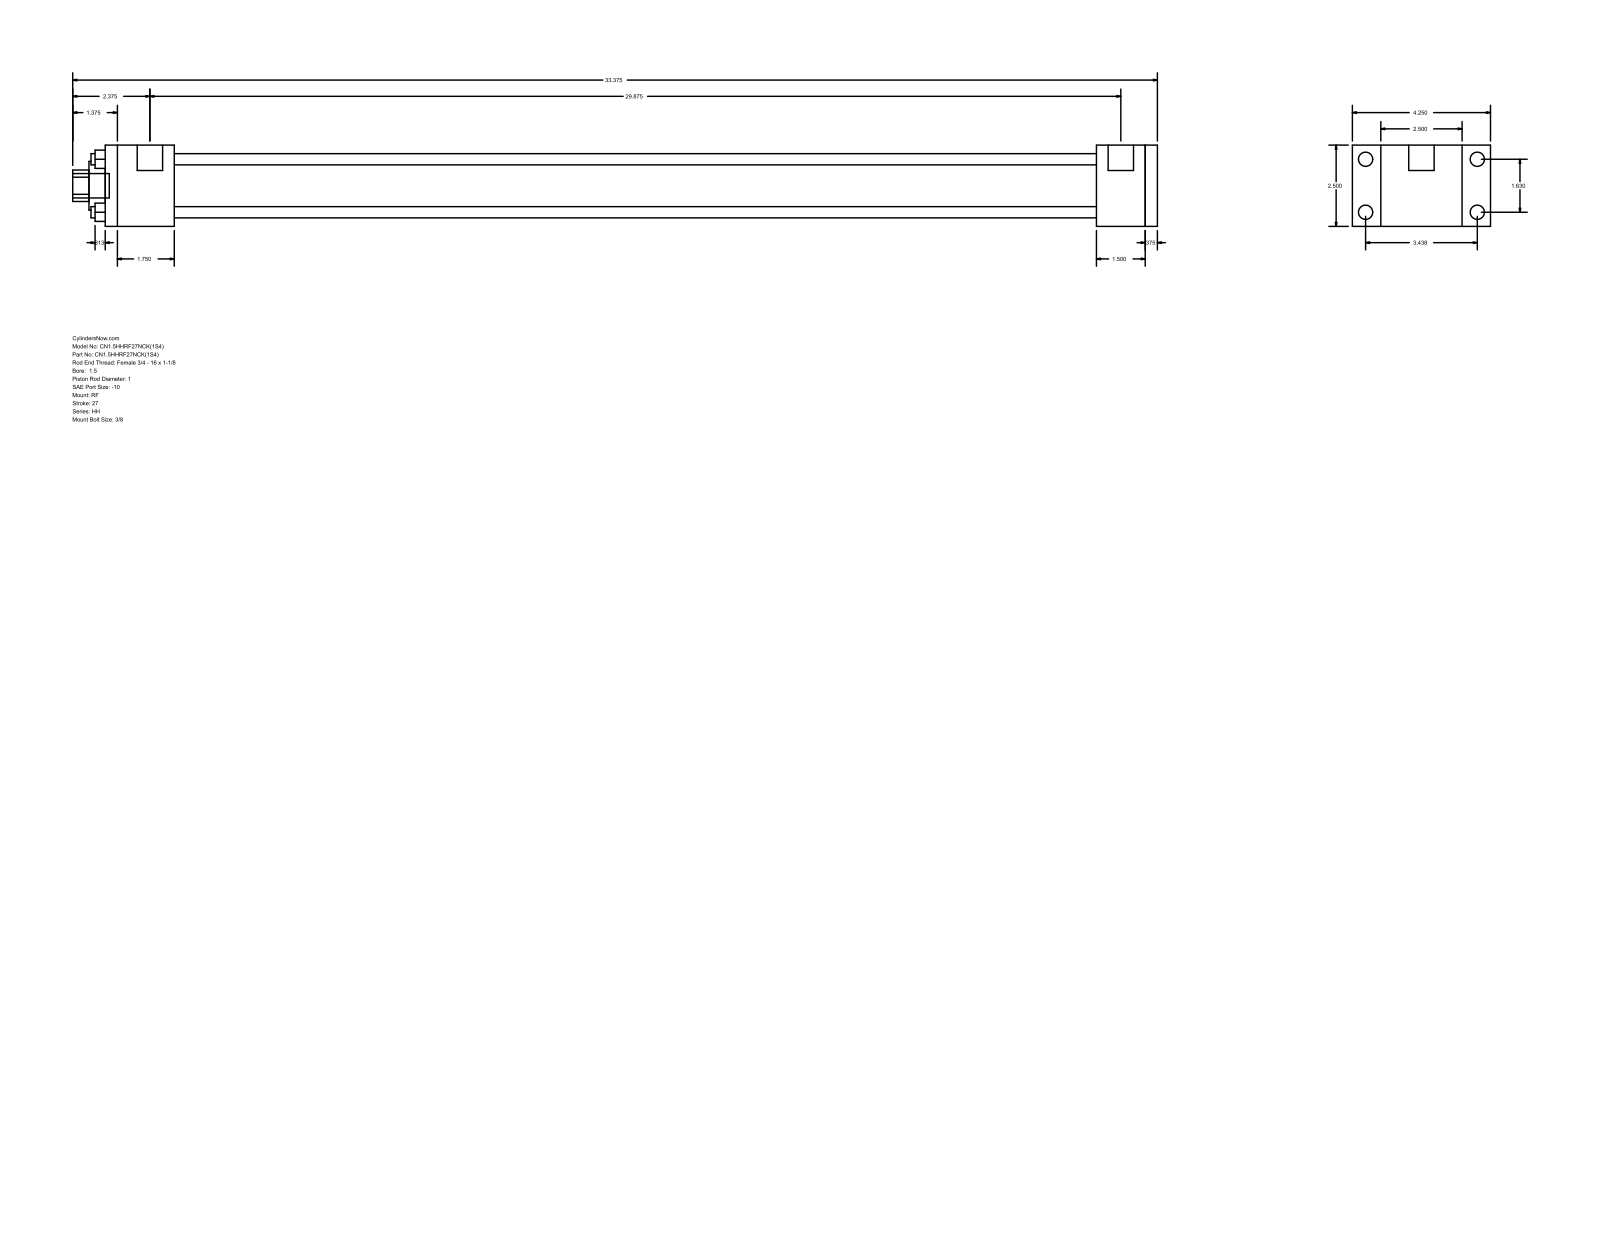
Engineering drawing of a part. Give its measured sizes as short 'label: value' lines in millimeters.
name: HH_RF__0150_1
written by: GSSL Pune (CONFIG_CONTROL_DESIGN)
unit: mm
bodies: 0 solids, 92 faces (64 planar, 28 cylindrical, 0 other)
size: 847.73 × 107.95 × 63.5
holes: 4× ⌀8.76, 1× ⌀25.4, 1× ⌀38.1, 1× ⌀44.45
bosses: 4× ⌀11.13, 4× ⌀5.56, 2× ⌀19.84, 1× ⌀19.05
rounds: 1× R12.29
face distances: 63.5, 9.53, 720.72, 758.82, 768.35, 38.1, 47.63, 53.98, 774.7, 812.8
hole spacings: 29.27, 41.4, 58.55
